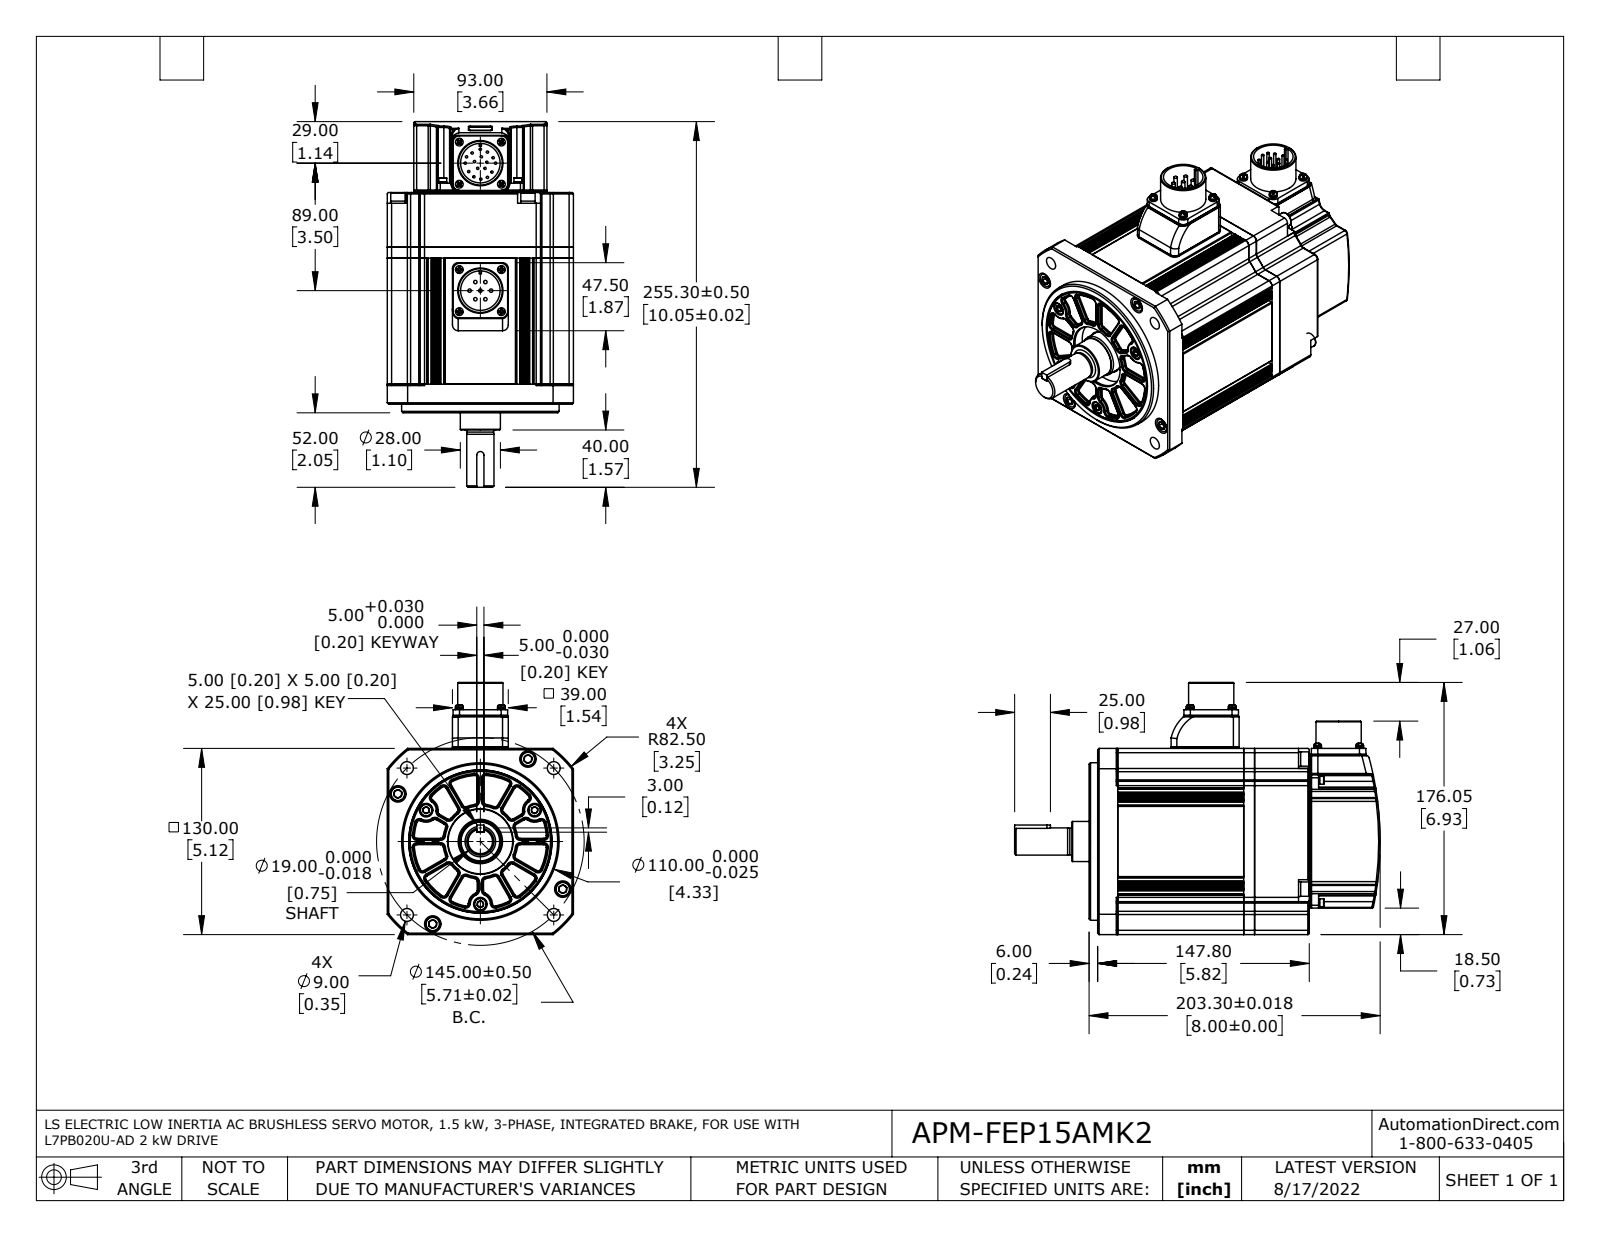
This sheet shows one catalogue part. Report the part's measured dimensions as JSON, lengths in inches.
{"part_name": "FMP13GA003G02_Out Line(APM-FEP15A_K2) r1 nc fxt", "step_written_by": "SolidWorks 2017 (AUTOMOTIVE_DESIGN)", "units": "inches", "bodies": {"solids": 57, "faces": 2214, "planar": 729, "cylindrical": 841, "other": 644}, "overall_size": [10.051, 6.931, 5.118], "volume_in3": 164.3, "surface_area_in2": 530.9, "round_holes": [[0.098, 12], [0.118, 8], [0.12, 8], [0.138, 8], [0.197, 7], [0.142, 4], [0.146, 4], [0.268, 4], [0.276, 4], [0.354, 4], [0.453, 4], [0.22, 3]], "round_bosses_or_shafts": [[0.063, 17], [0.213, 8], [0.094, 7], [0.402, 4], [0.394, 4], [0.236, 4], [0.217, 4], [0.118, 4]], "partial_cylinders_radius": [[0.02, 72], [0.098, 55], [0.028, 24], [0.039, 22], [0.079, 17], [0.118, 16], [0.177, 12], [0.157, 8]], "face_to_face_distances": [3.465, 0.299, 3.764, 0.039, 5.118, 5.327, 1.524, 1.823, 5.287, 1.563], "hole_center_spacings": [0.819, 1.157, 3.504, 0.752, 1.041, 1.637, 1.975, 2.618]}
